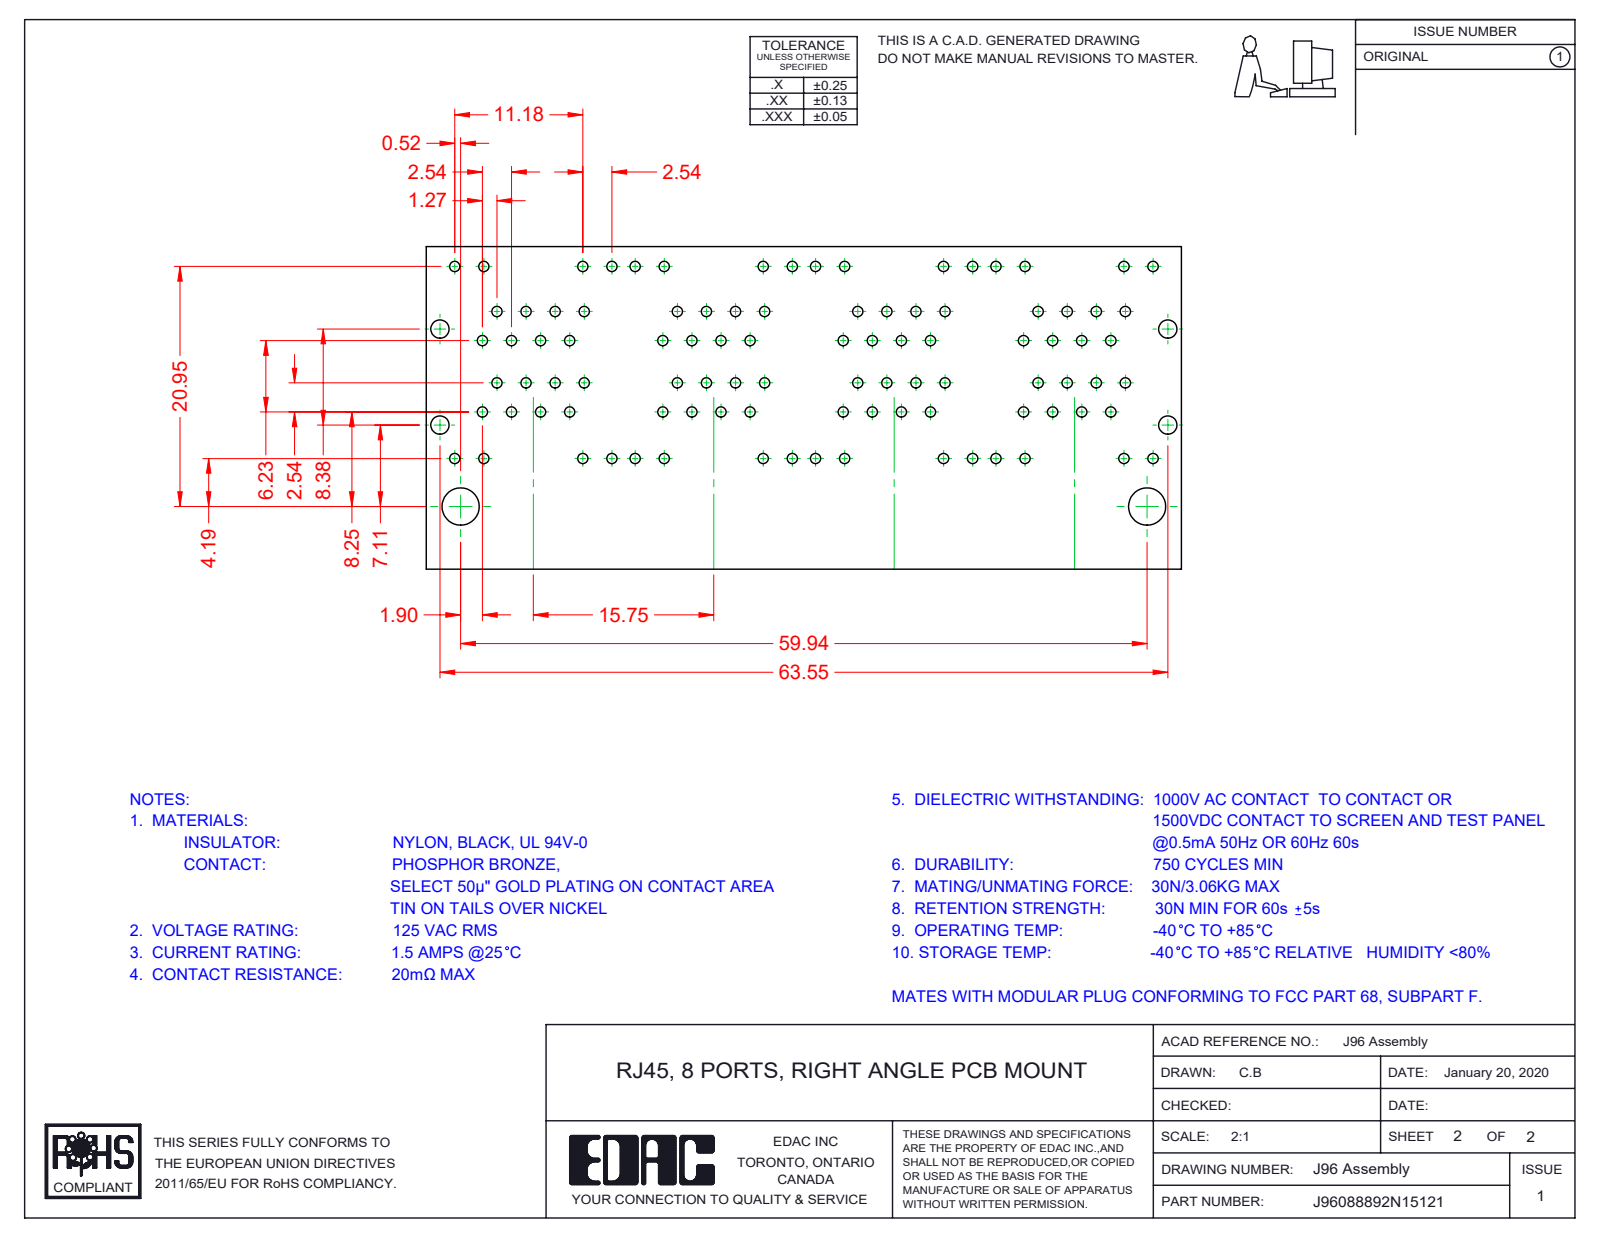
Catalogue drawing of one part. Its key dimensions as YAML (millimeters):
part_name: "J96088892N15121; 96 LED LH Upper_1-Yellow; 96 Shield_8 Ports LED - No EMI; 96 Contact Lock Upper (+8 more)"
step_written_by: "SolidWorks 2016 (CONFIG_CONTROL_DESIGN)"
units: millimeters
bodies: {solids: 96, faces: 7658, planar: 6069, cylindrical: 1323, other: 266}
overall_size: [64.05, 29.58, 28.68]
volume: 24160
surface_area: 63658
round_holes:
  - {diameter: 1.7, count: 3}
round_bosses_or_shafts:
  - {diameter: 1.68, count: 3}
partial_cylinders:
  - {radius: 0.25, count: 124}
  - {radius: 0.35, count: 73}
  - {radius: 1, count: 72}
  - {radius: 0.5, count: 49}
  - {radius: 0.91, count: 32}
  - {radius: 0.2, count: 21}
  - {radius: 0.7, count: 11}
  - {radius: 0.22, count: 8}
face_to_face_distances: [15.75, 0.35, 9.95, 1.17, 1.6, 0.54, 9.98, 10.18, 12.67, 3.37]
hole_center_spacings: [15.75, 31.5]
